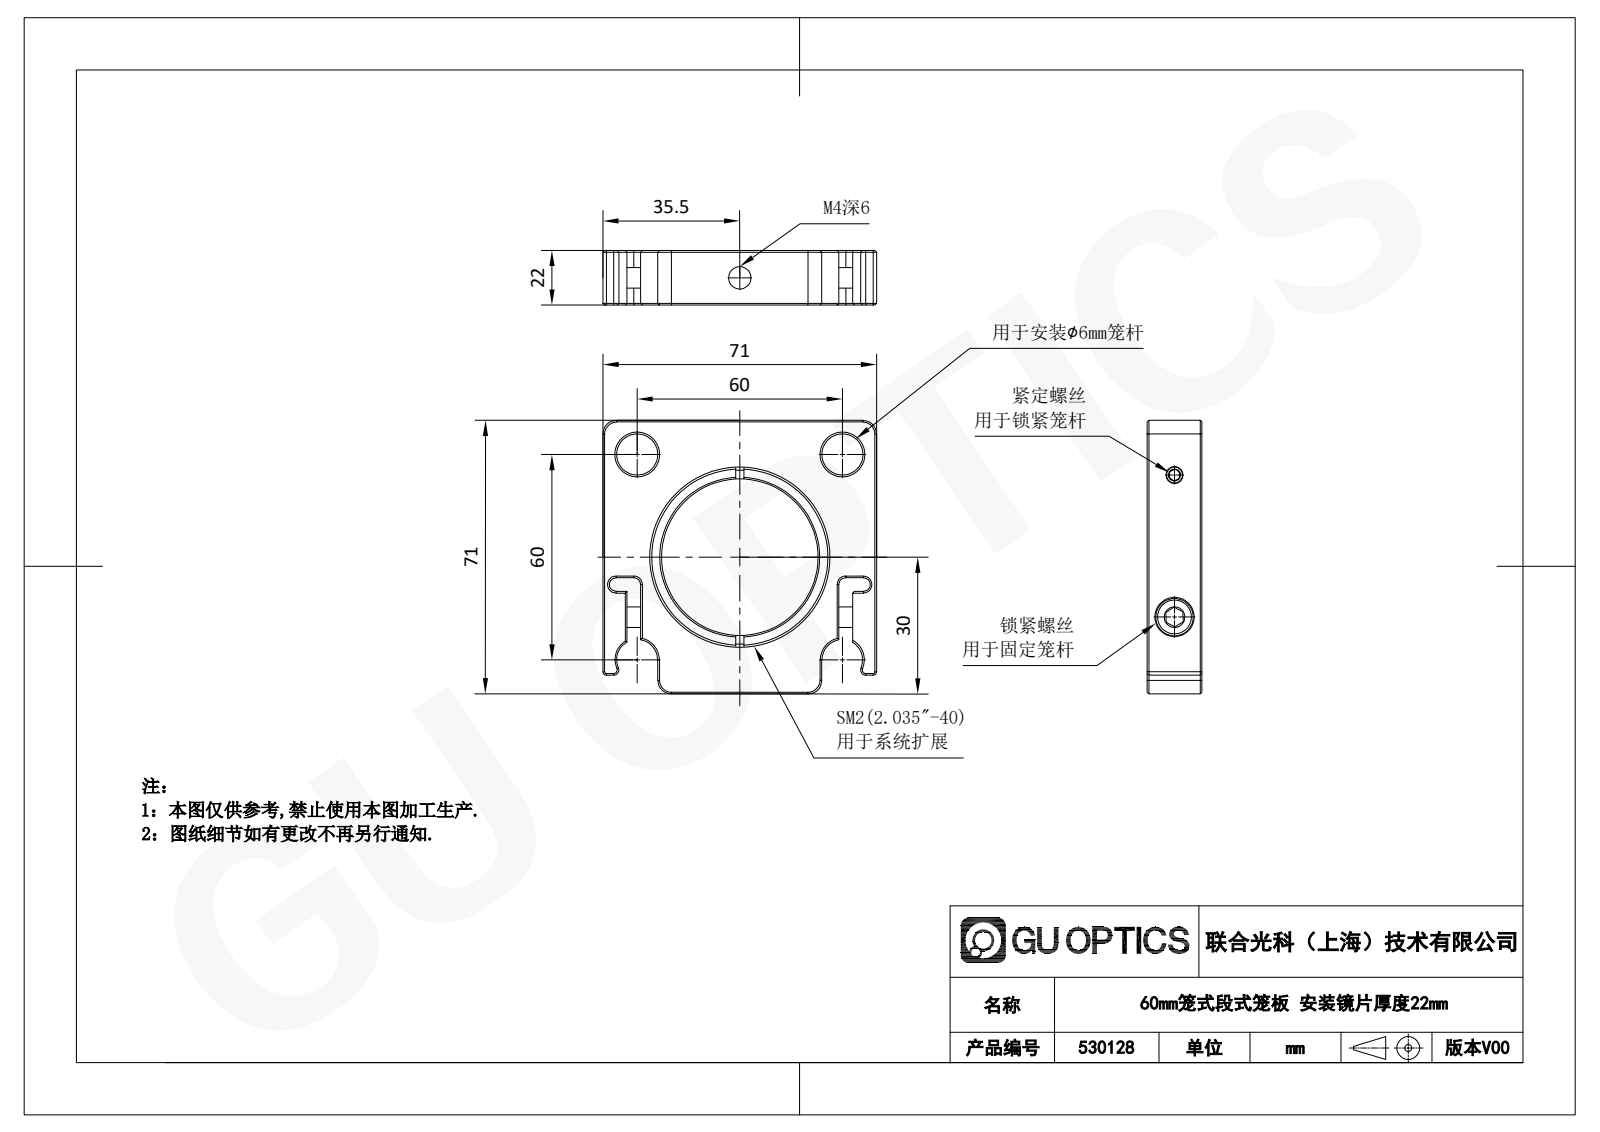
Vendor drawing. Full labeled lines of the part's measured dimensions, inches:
Part name (STEP PRODUCT): 530128
STEP written by: SolidWorks 2020 (CONFIG_CONTROL_DESIGN)
Units: inches
Bodies: 10 solids, 283 faces (139 planar, 40 cylindrical, 104 other)
Overall size (bounding box): 2.8 × 2.8 × 0.9
Volume: 3.794 in³ · Surface area: 33.22 in²
Round holes (diameter × count): ⌀0.098 ×3, ⌀0.236 ×2, ⌀0.25 ×2, ⌀0.13 ×1, ⌀0.134 ×1, ⌀0.236 ×1, ⌀1.902 ×1, ⌀2.035 ×1
Round bosses / shafts (diameter × count): ⌀0.118 ×3, ⌀2.035 ×1, ⌀0.217 ×1
Partial cylindrical surfaces — rounded edges, fillets, slot ends (radius × count): R0.1 ×2, R0.119 ×2, R0.125 ×2, R0.063 ×1, R0.063 ×1
Main face-to-face distances: 0.9, 2.8, 0.098, 0.266, 2.534, 0.802, 2.362, 0.172, 2.628, 0.094
Hole centre spacings: 1.67, 1.832, 2.05, 0.5, 1.404, 1.405, 2.362, 2.49
